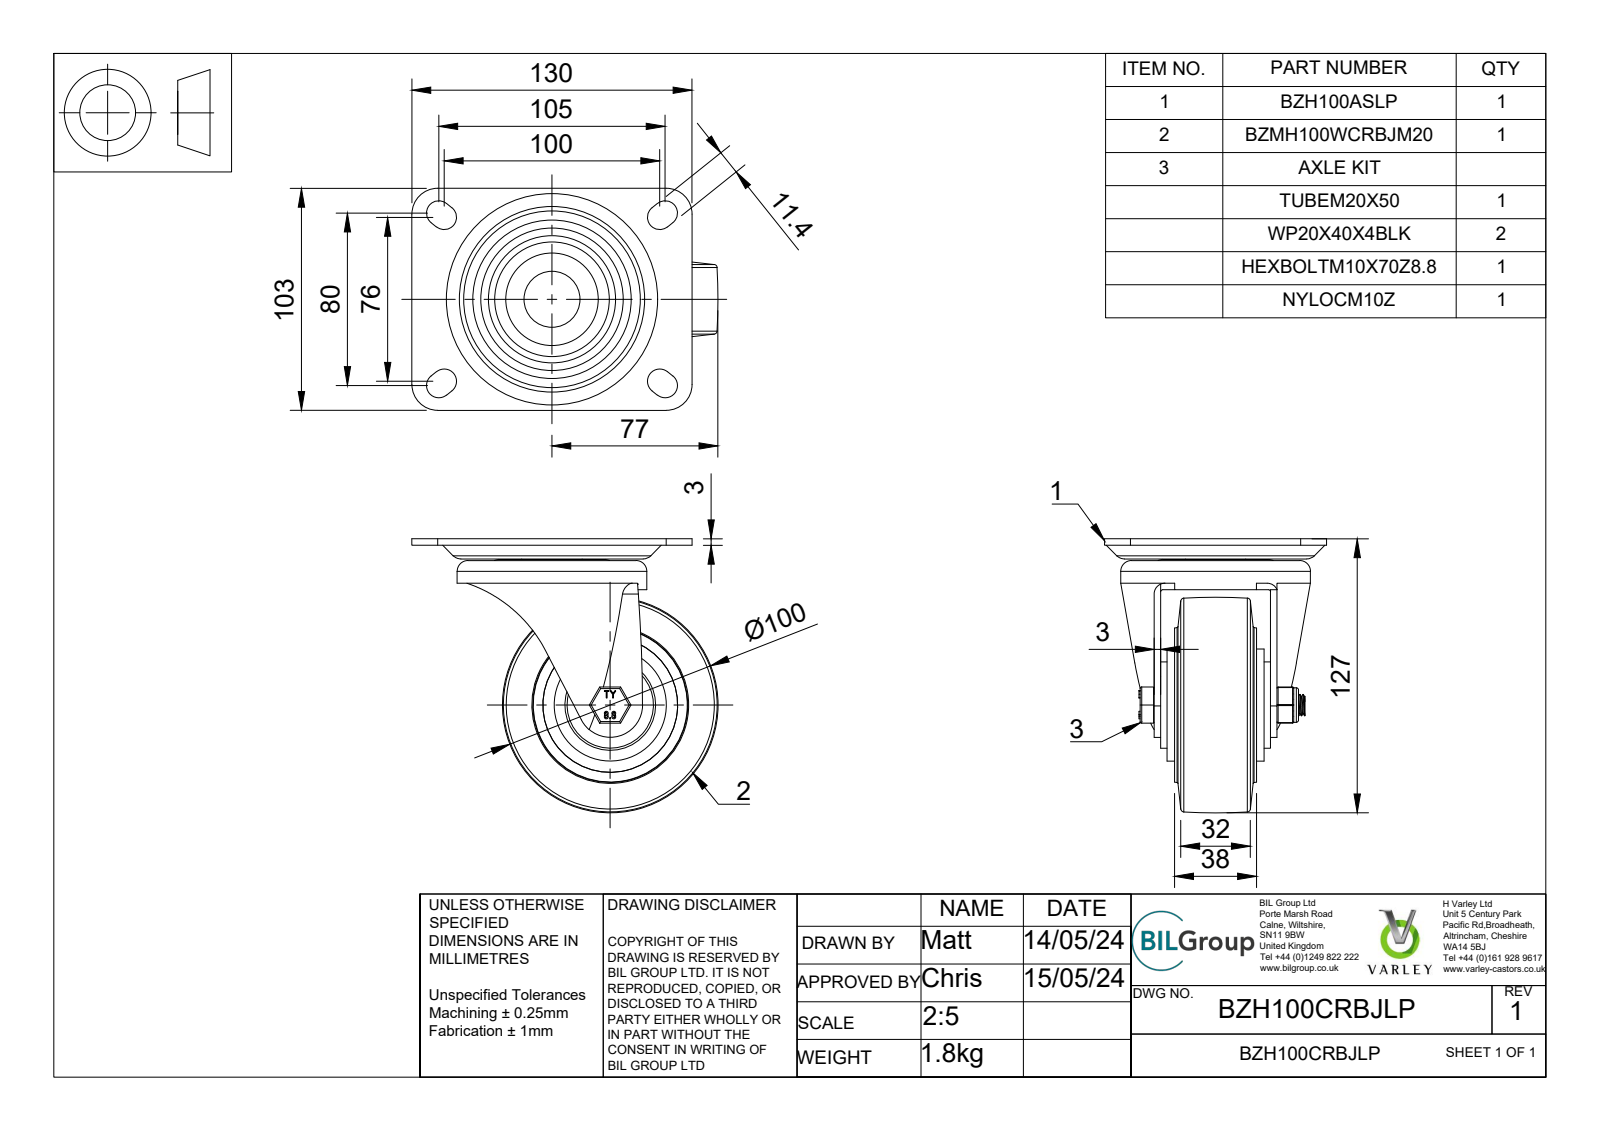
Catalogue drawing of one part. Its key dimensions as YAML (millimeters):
part_name: "BZH100CRBJLP v3; BZH100ASLP v1; ZINC PLATED PRESSED STEEL FORK; ZINC PLATED PRESSED STEEL TOP PLATE (+7 more)"
step_written_by: "Autodesk Translation Framework v13.14.0.145 (AUTOMOTIVE_DESIGN)"
units: millimeters
bodies: {solids: 39, faces: 1180, planar: 441, cylindrical: 219, other: 520}
overall_size: [142, 127.13, 103]
volume: 374944
surface_area: 150201
round_holes:
  - {diameter: 10, count: 1}
  - {diameter: 10.5, count: 1}
  - {diameter: 12, count: 1}
  - {diameter: 20, count: 1}
  - {diameter: 21, count: 1}
  - {diameter: 25, count: 1}
  - {diameter: 26, count: 1}
  - {diameter: 30, count: 1}
  - {diameter: 35, count: 1}
  - {diameter: 36, count: 1}
  - {diameter: 38, count: 1}
  - {diameter: 42, count: 1}
round_bosses_or_shafts:
  - {diameter: 8, count: 18}
  - {diameter: 88, count: 1}
  - {diameter: 52, count: 1}
  - {diameter: 40, count: 1}
  - {diameter: 37, count: 1}
  - {diameter: 36, count: 1}
  - {diameter: 28, count: 1}
  - {diameter: 27, count: 1}
partial_cylinders:
  - {radius: 0.5, count: 18}
  - {radius: 5.7, count: 8}
  - {radius: 0.75, count: 6}
  - {radius: 12, count: 4}
  - {radius: 1, count: 2}
  - {radius: 5, count: 2}
  - {radius: 15, count: 1}
  - {radius: 16.75, count: 1}
face_to_face_distances: [3, 51, 6.5, 44.5, 3.5, 0.7, 0.5, 33, 2.8, 4]
